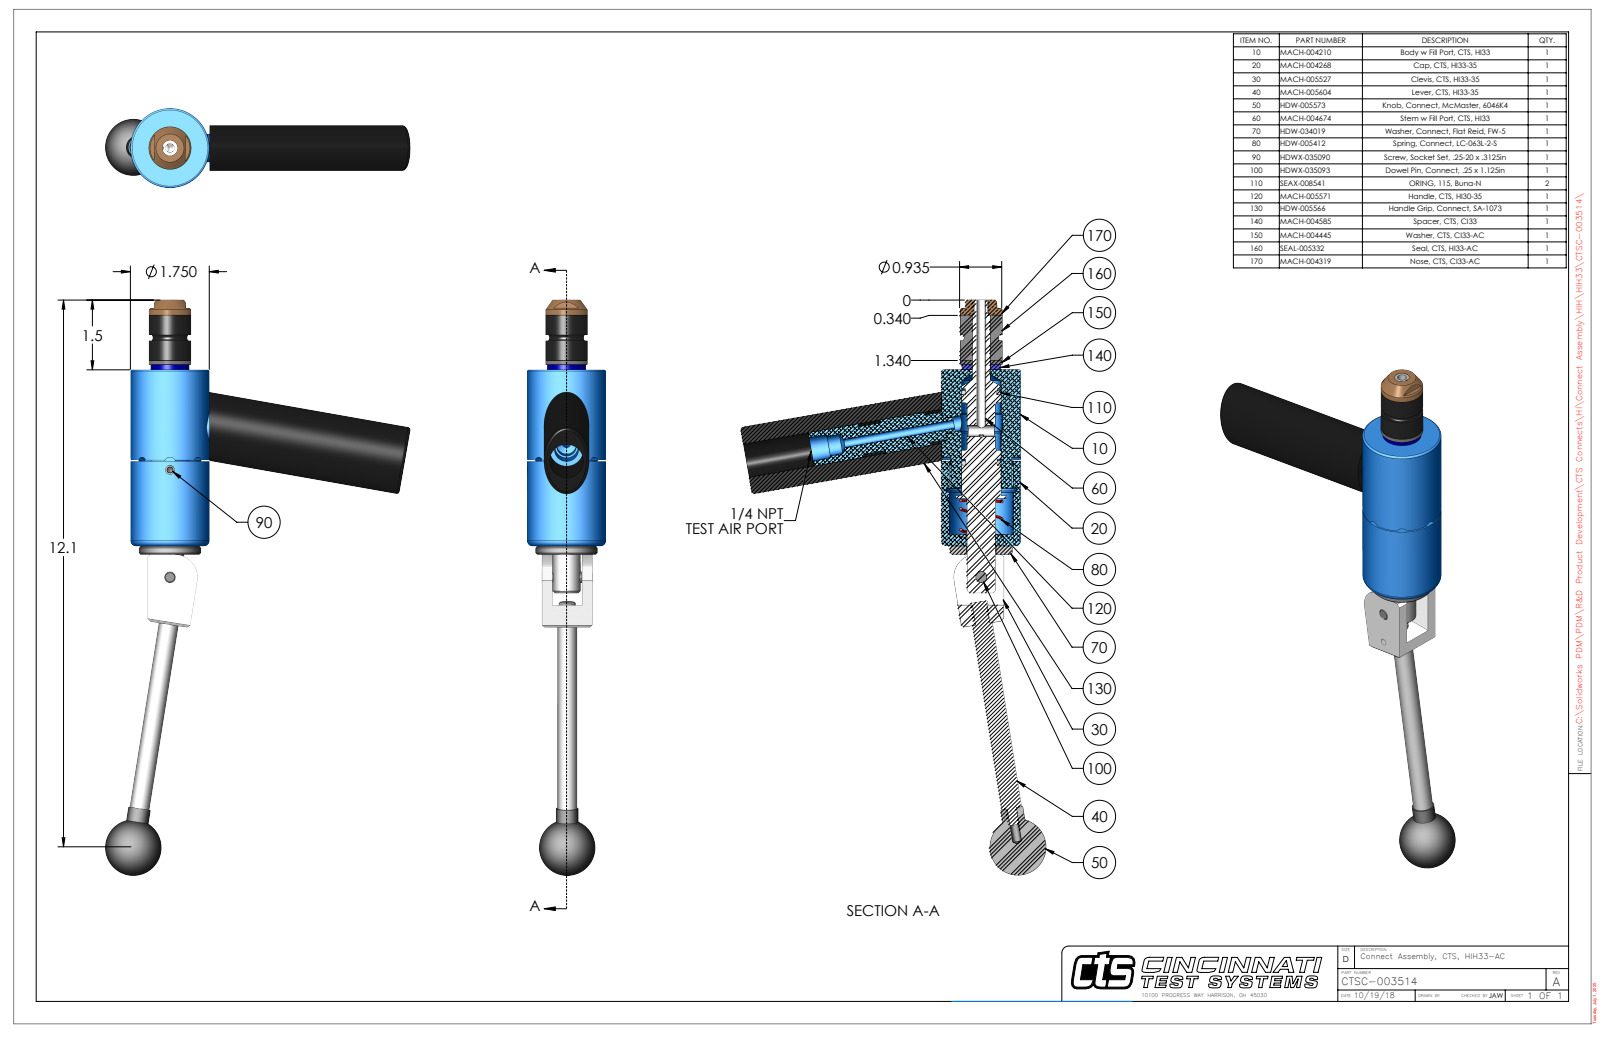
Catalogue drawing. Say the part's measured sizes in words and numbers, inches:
The part is named "CTSC-003514". Its 3-D file was written by "SolidWorks 2023 (AUTOMOTIVE_DESIGN)". It is 11 solids with 288 faces: 93 planar, 126 cylindrical and 69 other. Overall it measures 12.751 by 6.763 by 1.75 inches. Its volume is 17.73 cubic inches and its surface area 111.2 square inches. Round holes: 2 of diameter 0.201, 2 of diameter 0.313, 1 of diameter 0.15, 1 of diameter 0.187, 1 of diameter 0.204, 1 of diameter 0.249, 1 of diameter 0.25, 1 of diameter 0.251, 1 of diameter 0.39, 1 of diameter 0.397, 1 of diameter 0.403, 1 of diameter 0.438. Round bosses or shafts: 2 of diameter 0.375, 2 of diameter 0.312, 2 of diameter 0.25, 1 of diameter 1.75, 1 of diameter 1.38, 1 of diameter 0.935, 1 of diameter 0.858, 1 of diameter 0.75. Partial cylindrical surfaces (rounded edges, fillets, slot ends): 4 of radius 0.125, 2 of radius 0.029, 1 of radius 0.145, 1 of radius 0.33, 1 of radius 0.5, 1 of radius 0.695, 1 of radius 0.826. The main face-to-face distances are 3.907, 1.12, 4.095, 0.188, 1.207, 5.114, 5.302, 1, 0.232, 0.888. The hole center spacings are 0.74, 2.376, 3.116.
